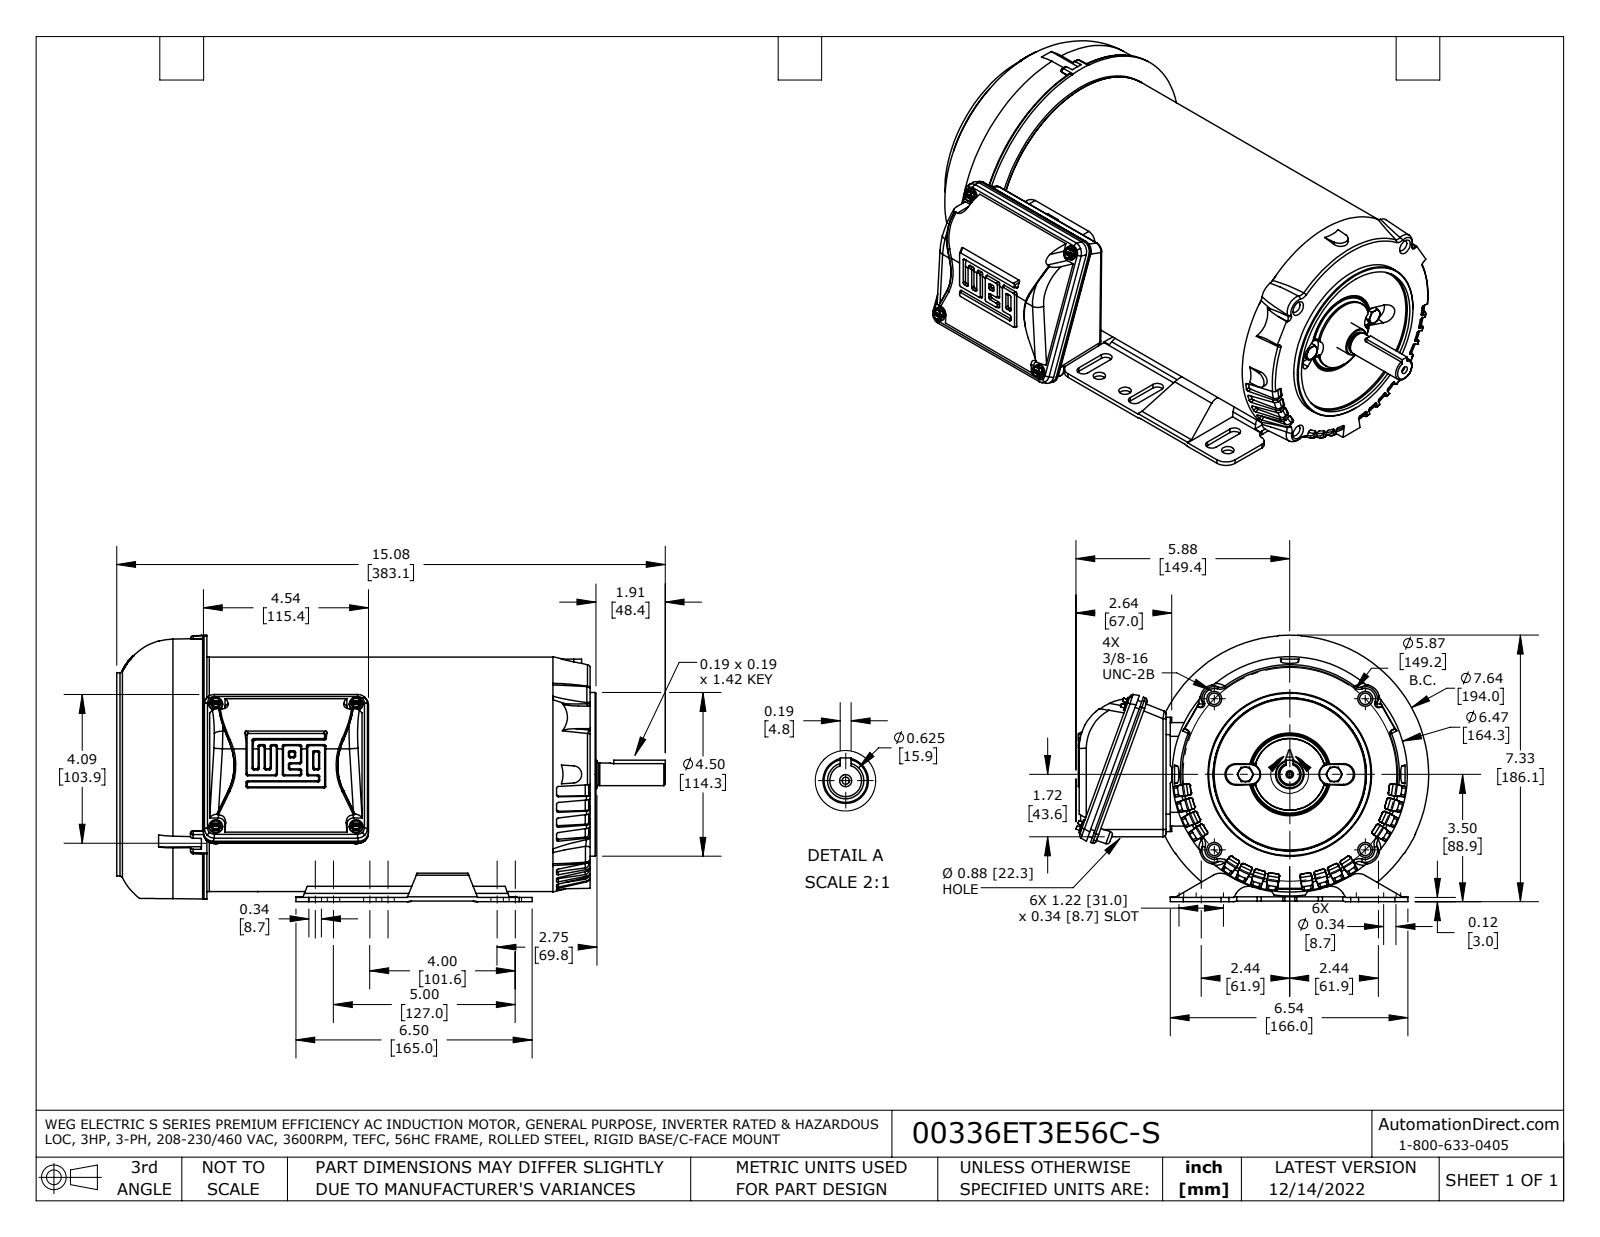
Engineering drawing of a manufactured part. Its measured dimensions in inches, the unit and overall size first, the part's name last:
Units: inches
Overall size (bounding box): 15.083 × 9.7 × 7.551
Round holes (diameter × count): ⌀0.343 ×6, ⌀0.313 ×4, ⌀0.124 ×1
Round bosses / shafts (diameter × count): ⌀0.374 ×4, ⌀0.35 ×2, ⌀6.447 ×1, ⌀6.447 ×1, ⌀5.591 ×1, ⌀4.5 ×1, ⌀1.575 ×1, ⌀0.783 ×1
Partial cylindrical surfaces — rounded edges, fillets, slot ends (radius × count): R0.047 ×40, R0.006 ×38, R0.051 ×32, R0.059 ×12, R0.087 ×12, R0.171 ×12, R0.02 ×10, R0.079 ×8
Main face-to-face distances: 9.449, 0.12, 0.067, 9.516, 2.283, 2.35, 11.799, 12.823, 10.539, 10.472
Hole centre spacings: 2.937, 4.154, 5.5, 1, 4, 5, 5.59, 5.874
Volume: 477.1 in³ · Surface area: 758.1 in²
Bodies: 15 solids, 1489 faces (559 planar, 357 cylindrical, 573 other)
Part name (STEP PRODUCT): 56HC_3PH_TEFC_GP_15079 new 09-26-22 broken base surfs w 1PHNB fxt
STEP written by: SolidWorks 2021 (AUTOMOTIVE_DESIGN)
